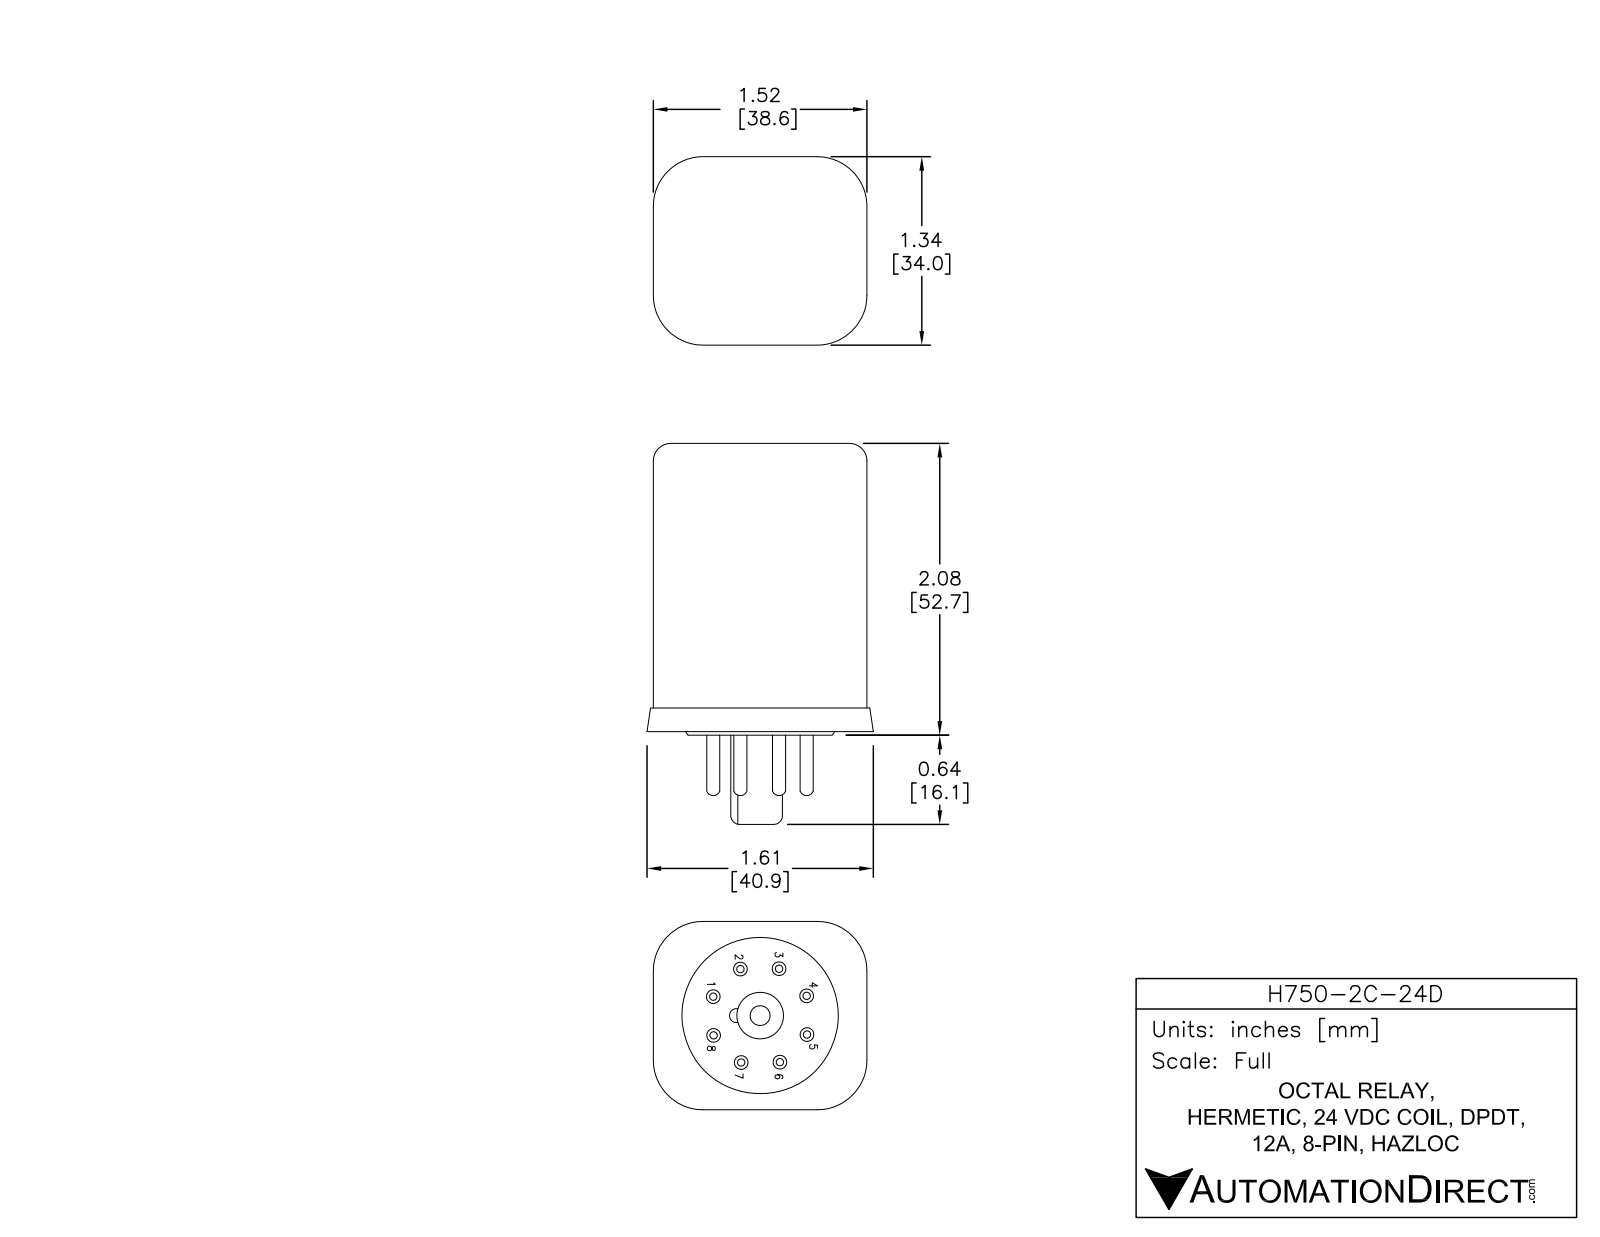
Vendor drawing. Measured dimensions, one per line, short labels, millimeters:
name: H750-2C-24D
written by: SolidWorks 2013 (AUTOMOTIVE_DESIGN)
unit: mm
bodies: 1 solid, 276 faces (118 planar, 65 cylindrical, 93 other)
size: 67.3 × 41.35 × 36.6
volume: 66 961 mm³; area: 10 714 mm²
holes: 8× ⌀4.5, 1× ⌀3.9
bosses: 8× ⌀2.31, 1× ⌀27, 1× ⌀12, 1× ⌀8
rounds: 8× R0.62, 4× R2.5, 4× R10, 4× R11.3, 2× R0.5, 1× R0.59
face distances: 53, 34, 38.75, 0.5, 53.5, 1.3, 35.3, 40.05, 1, 54
hole spacings: 8.5, 12.02, 15.7, 6.5, 6.51, 16.99
